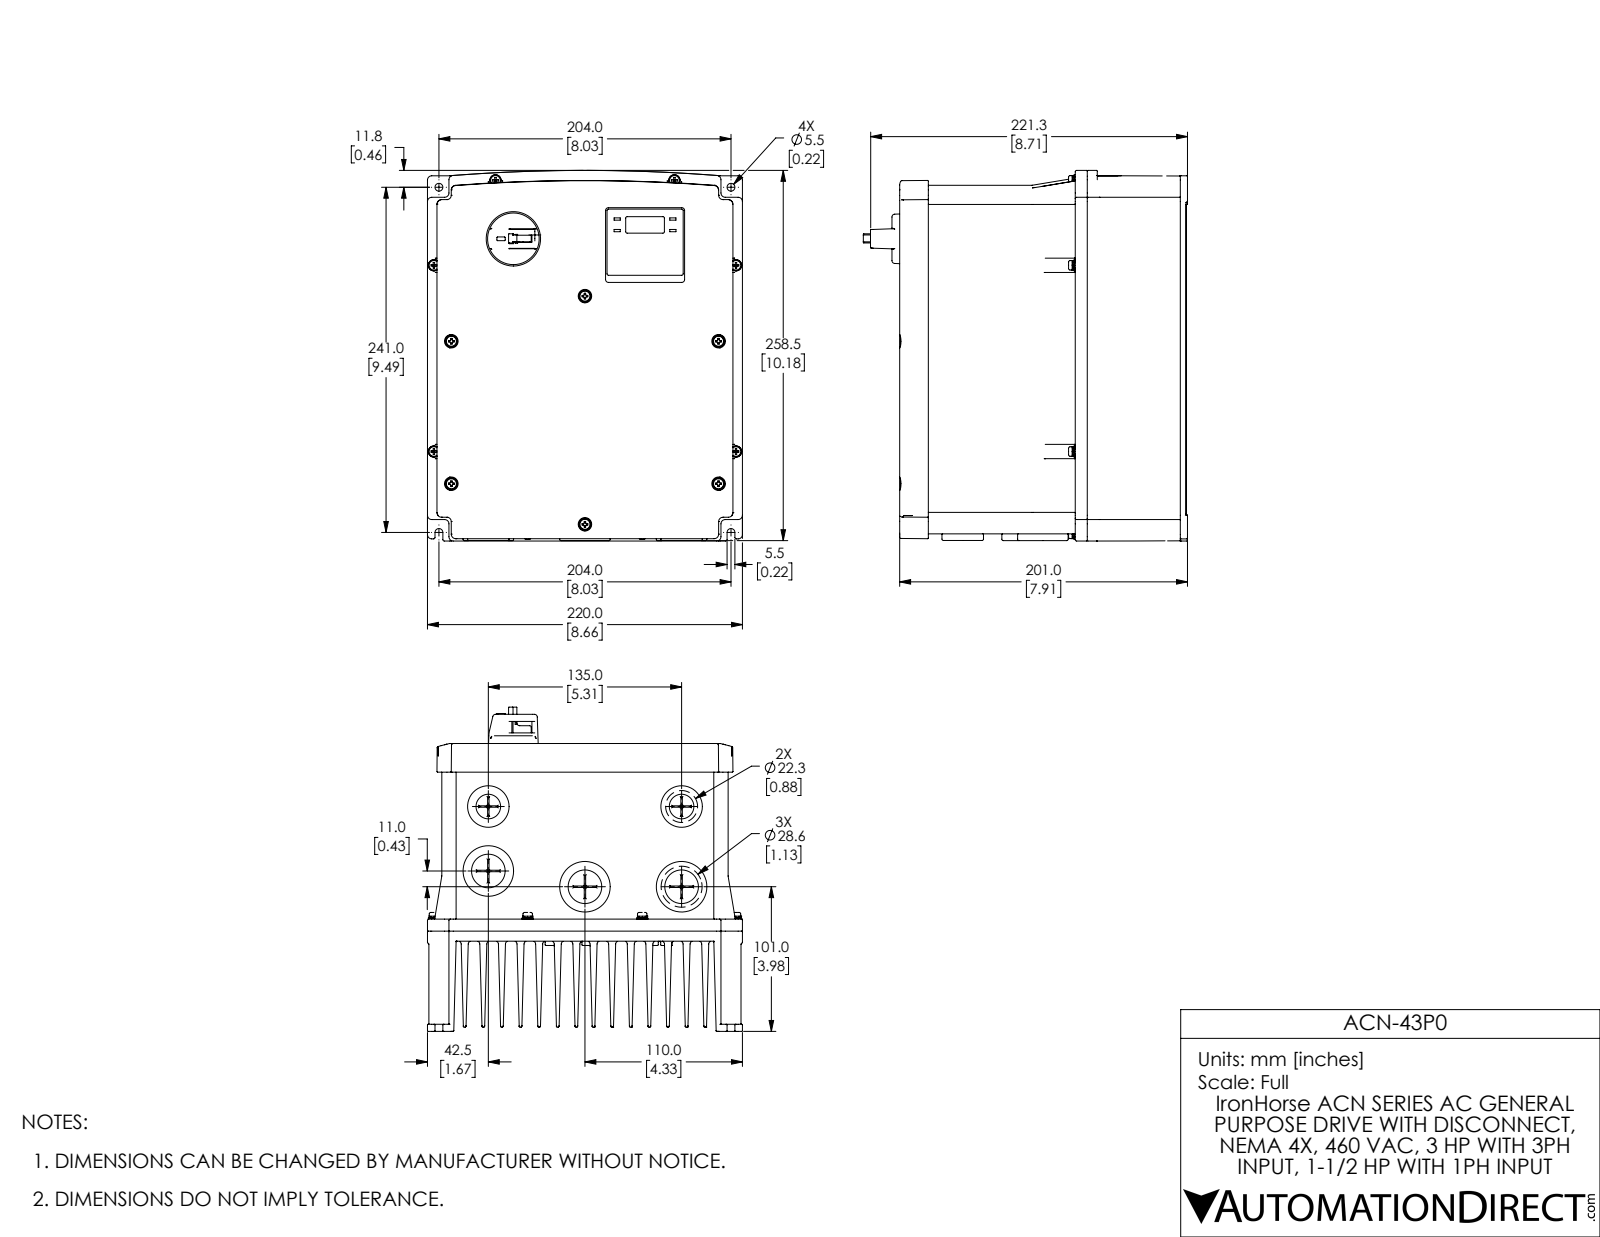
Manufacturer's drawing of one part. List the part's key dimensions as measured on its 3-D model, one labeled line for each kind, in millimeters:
Part name (STEP PRODUCT): ACN-22P0 KN
STEP written by: SolidWorks 2017 (AUTOMOTIVE_DESIGN)
Units: millimetres
Bodies: 19 solids, 3504 faces (1164 planar, 1122 cylindrical, 1218 other)
Overall size (bounding box): 258.77 × 226.4 × 220
Volume: 7 475 000 mm³ · Surface area: 842 809 mm²
Round holes (diameter × count): ⌀4 ×18, ⌀4.5 ×8, ⌀3 ×6, ⌀8.4 ×6, ⌀23.5 ×3, ⌀28.6 ×3, ⌀32.3 ×3, ⌀3.6 ×2, ⌀5 ×2, ⌀5.5 ×2, ⌀17.2 ×2, ⌀22.3 ×2
Round bosses / shafts (diameter × count): ⌀7.9 ×8, ⌀6.7 ×8, ⌀8 ×6, ⌀35.3 ×3, ⌀27.9 ×3, ⌀29 ×2, ⌀21.6 ×2, ⌀14 ×1
Partial cylindrical surfaces — rounded edges, fillets, slot ends (radius × count): R0.5 ×287, R2 ×83, R3 ×62, R0.3 ×53, R1 ×47, R0.2 ×21, R5 ×8, R4.25 ×5
Main face-to-face distances: 13, 26, 39, 90, 52, 103, 77, 116, 64, 65
Hole centre spacings: 72, 149.92, 131.5, 144.68, 25.59, 39.79, 40.56, 54.39
